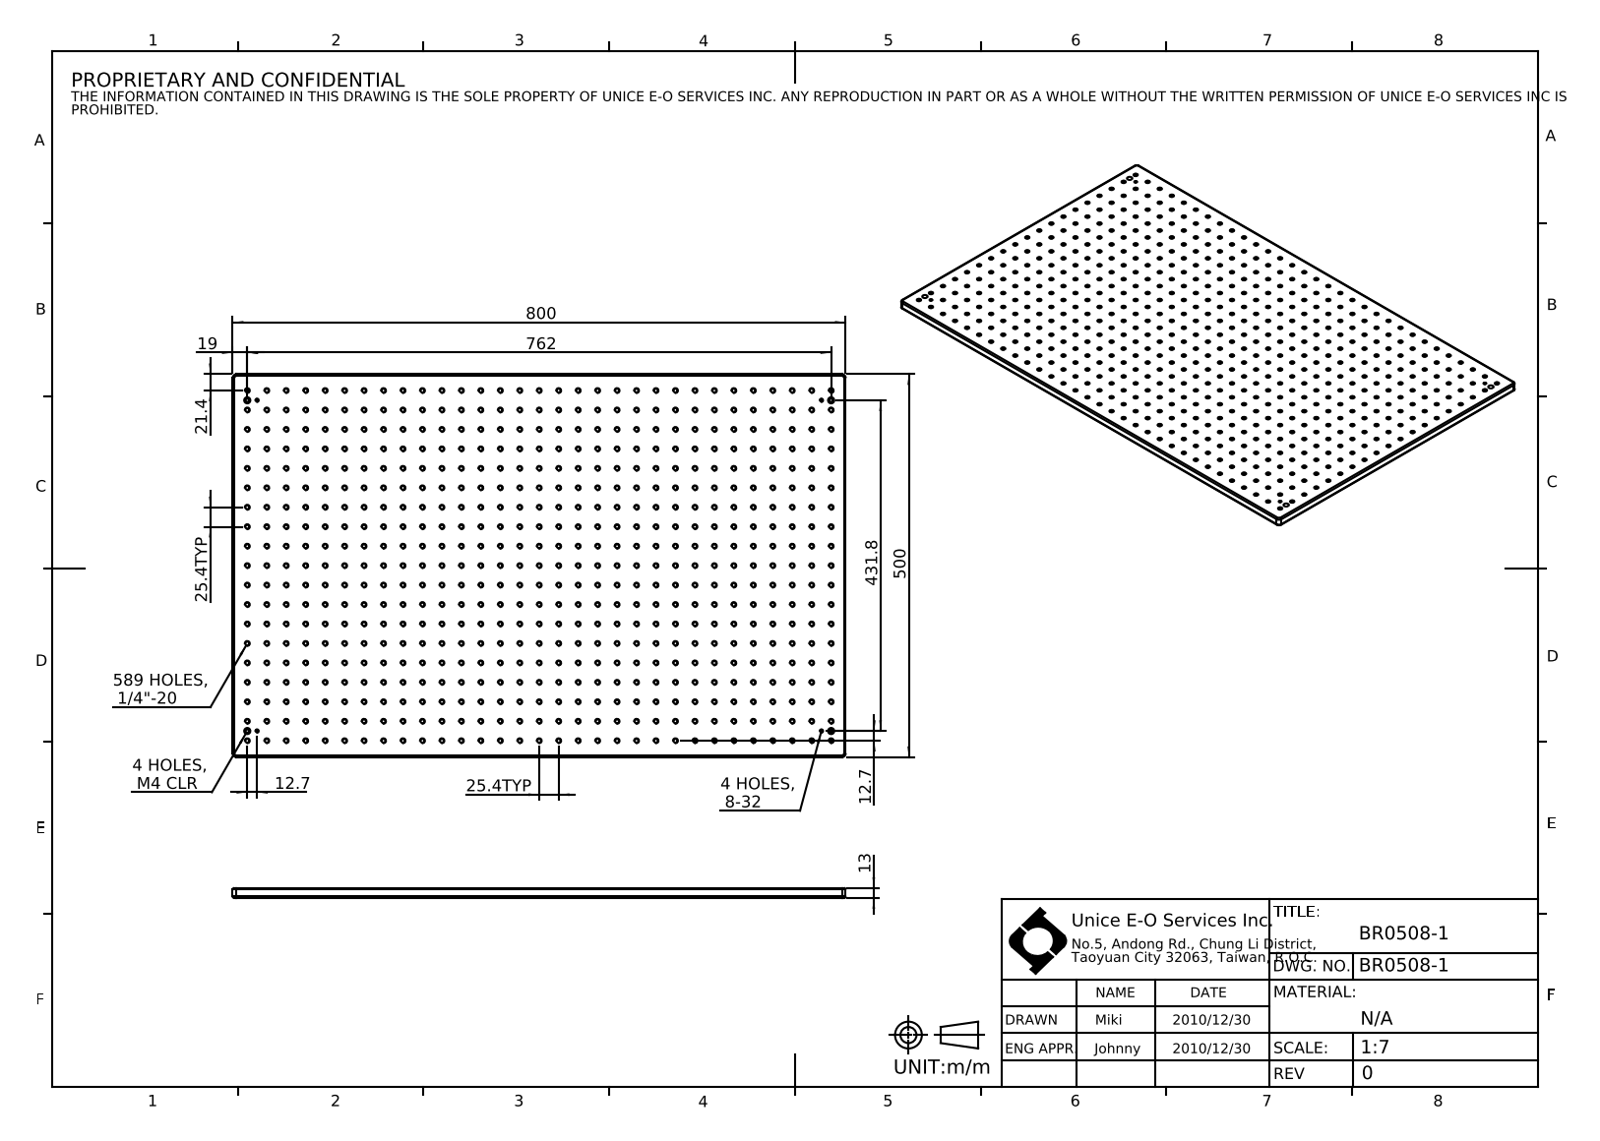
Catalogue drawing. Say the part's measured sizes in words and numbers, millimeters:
The part is named "BR0508-1". Its 3-D file was written by "SolidWorks 2016 (CONFIG_CONTROL_DESIGN)". It is 1 solid with 1232 faces: 10 planar, 1214 cylindrical and 8 other. Overall it measures 800 by 500 by 13 millimeters. Its volume is 5 036 000 cubic millimeters and its surface area 929 250 square millimeters. Round holes: 589 of diameter 5.11, 4 of diameter 3.45, 4 of diameter 4.5, 4 of diameter 8. Partial cylindrical surfaces (rounded edges, fillets, slot ends): 8 of radius 2, 4 of radius 5. The main face-to-face distances are 13, 500, 800, 7, 6. The hole center spacings are 25.4, 50.8, 76.2, 101.6, 127, 152.4, 177.8, 203.2.
